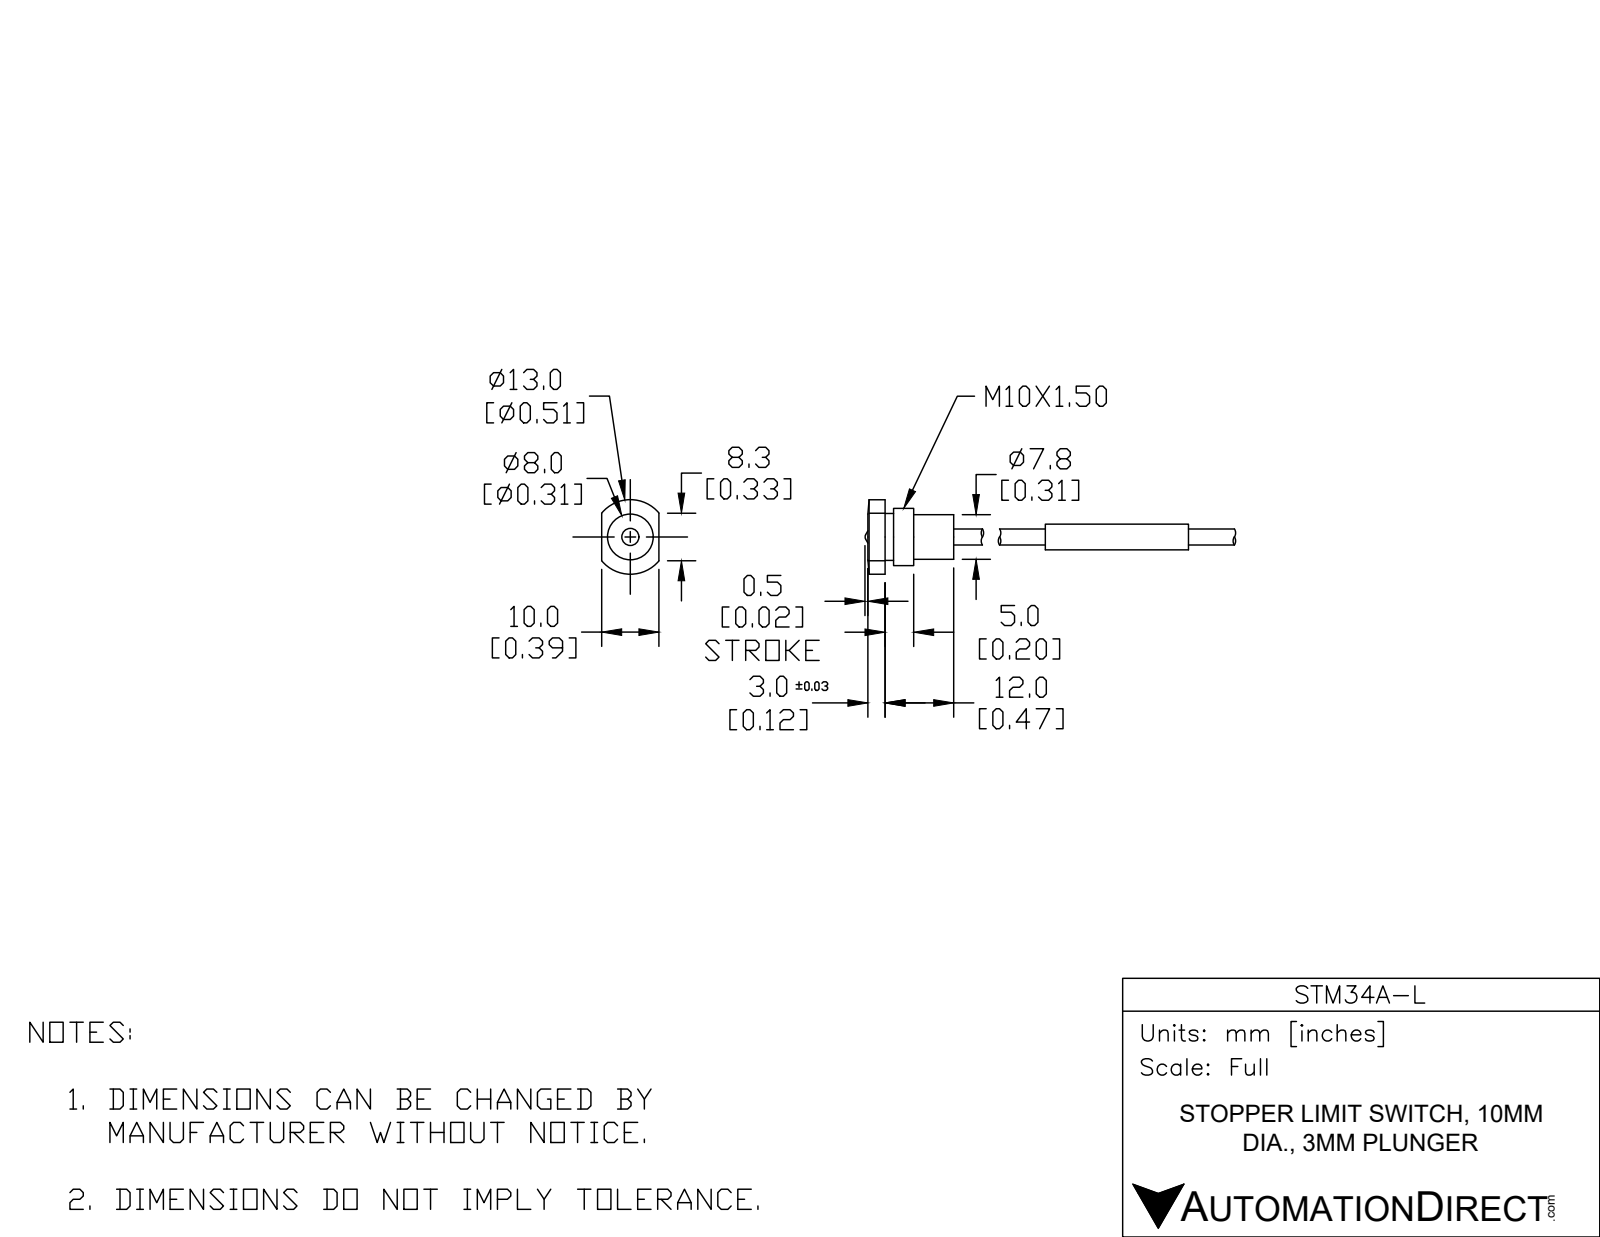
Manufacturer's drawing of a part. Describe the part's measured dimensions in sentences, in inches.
The part is named "STM34A-L". Its 3-D file was written by "SolidWorks 2017 (CONFIG_CONTROL_DESIGN)". It is 2 solids with 41 faces: 12 planar, 20 cylindrical and 9 other. Overall it measures 2.618 by 0.512 by 0.394 inches. Its volume is 0.093 cubic inches and its surface area 2.069 square inches. Round bosses or shafts: 1 of diameter 0.394, 1 of diameter 0.323, 1 of diameter 0.307, 1 of diameter 0.177, 1 of diameter 0.11. Partial cylindrical surfaces (rounded edges, fillets, slot ends): 1 of radius 0.256. The main face-to-face distances are 0.118, 0.591, 0.472, 0.394, 0.276, 0.315, 0.197, 0.63, 0.177, 0.059.
